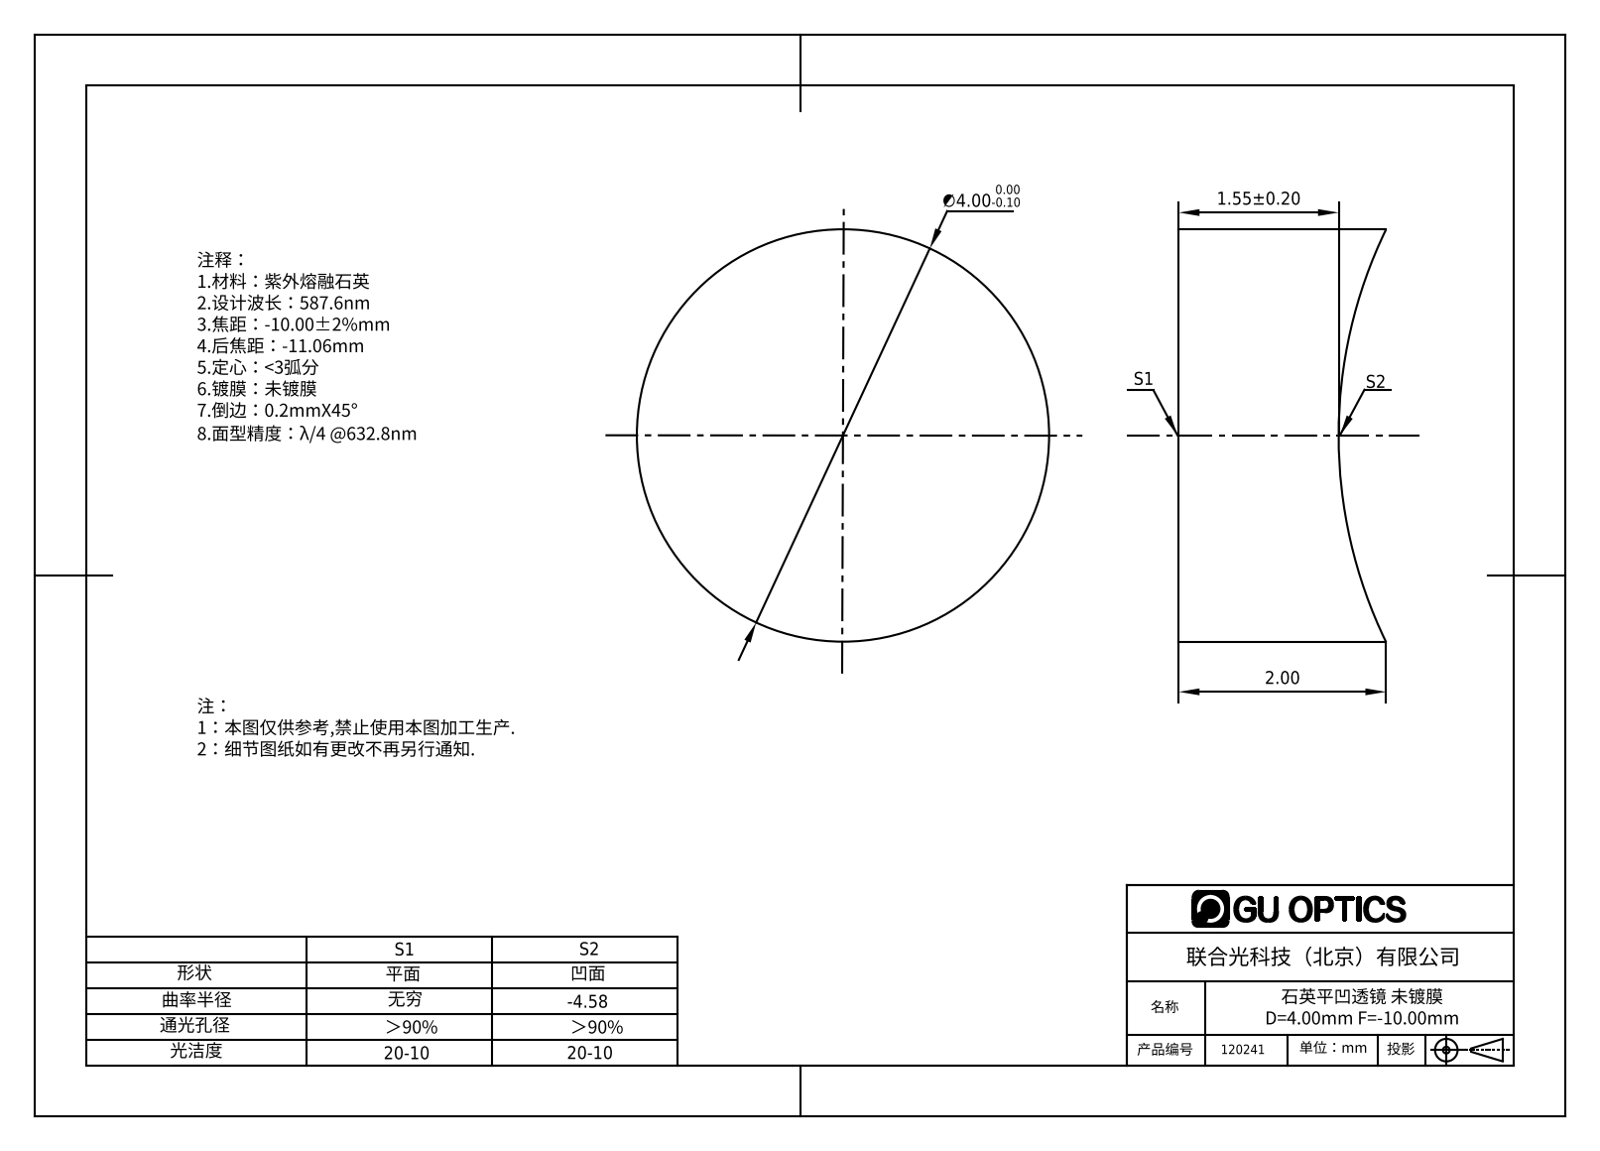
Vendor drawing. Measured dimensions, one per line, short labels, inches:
name: 120241
written by: SolidWorks 2016 (AUTOMOTIVE_DESIGN)
unit: in
bodies: 1 solid, 5 faces (1 planar, 2 cylindrical, 2 other)
size: 0.157 × 0.157 × 0.077
volume: 0.001 in³; area: 0.078 in²
bosses: 1× ⌀0.157
